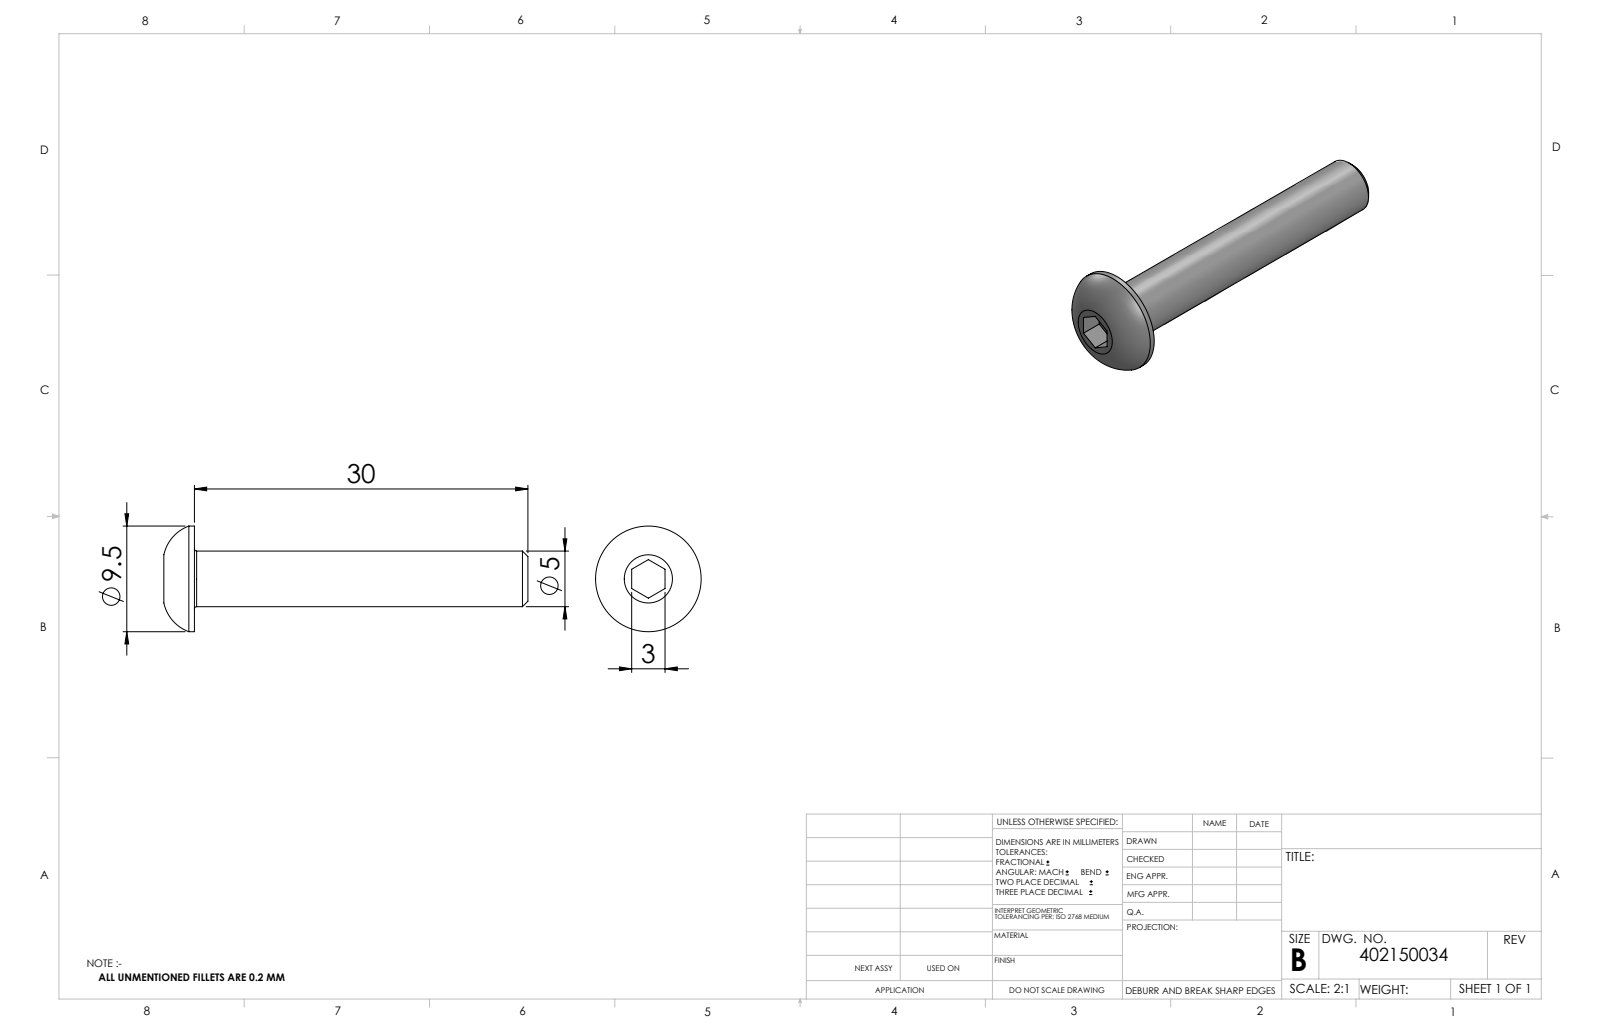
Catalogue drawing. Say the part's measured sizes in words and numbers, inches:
The part is named "402150034_c_1". Its 3-D file was written by "SolidWorks 2014 (CONFIG_CONTROL_DESIGN)". It is 1 solid with 20 faces: 10 planar, 4 cylindrical and 6 other. Overall it measures 1.289 by 0.374 by 0.374 inches. Its volume is 0.044 cubic inches and its surface area 1.04 square inches. Round bosses or shafts: 1 of diameter 0.374, 1 of diameter 0.197. The main face-to-face distances are 1.181, 0.118, 1.211, 0.03, 1.289, 0.108, 0.079.
